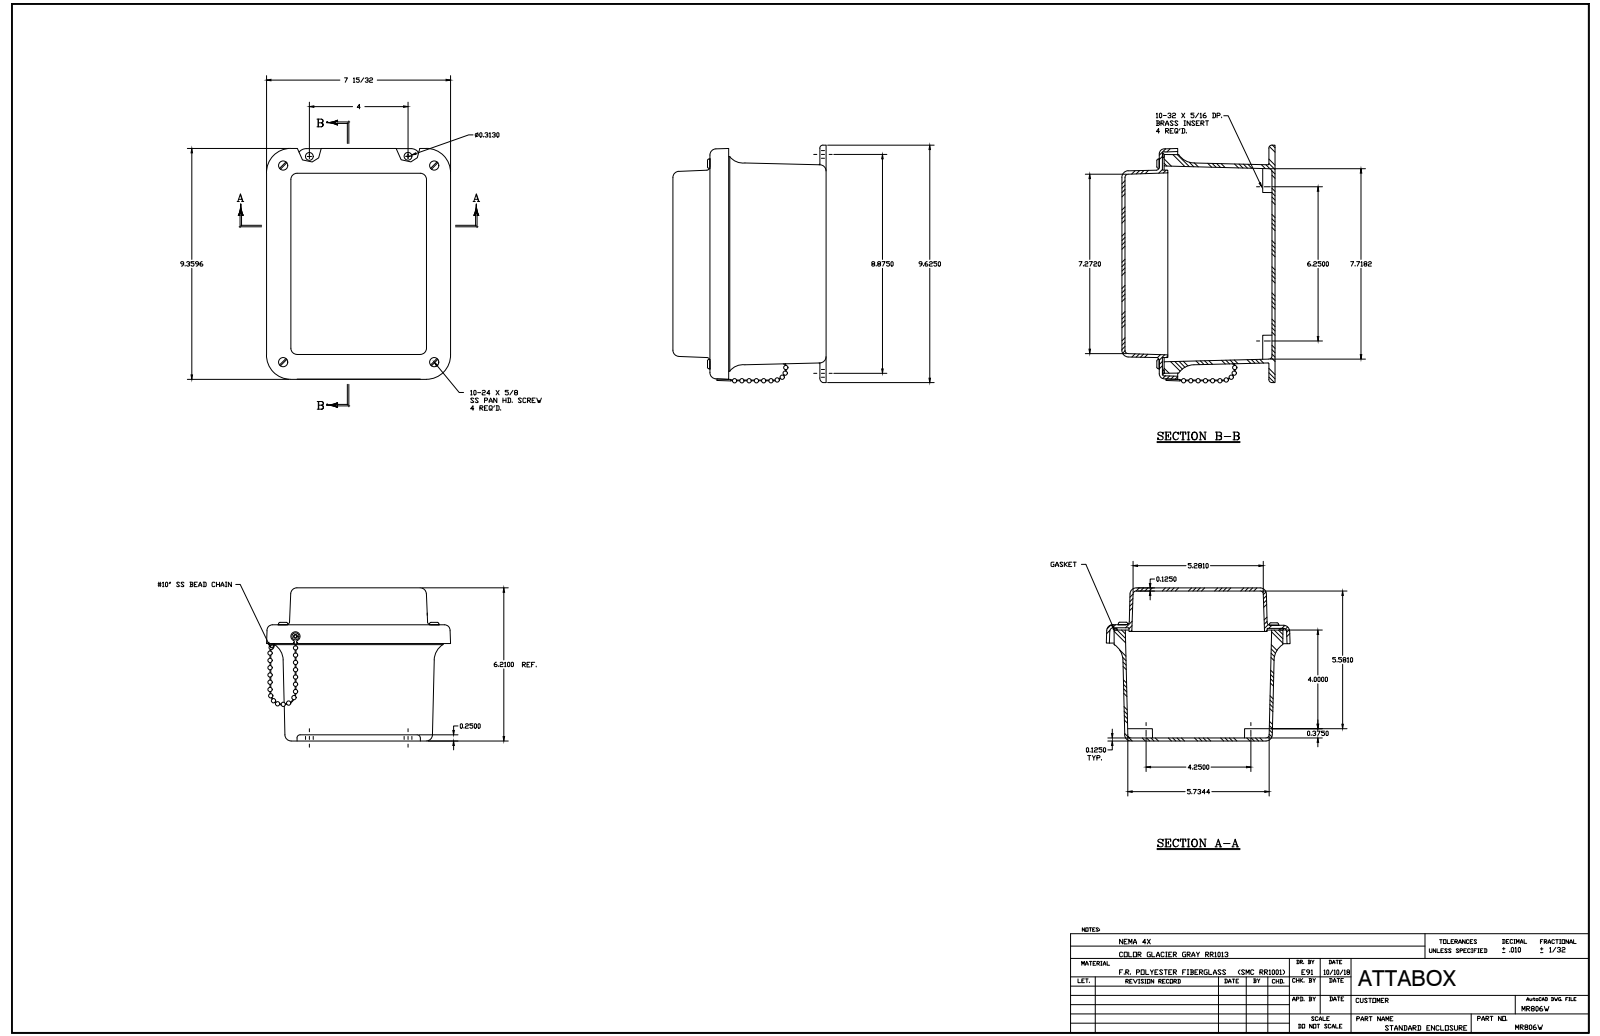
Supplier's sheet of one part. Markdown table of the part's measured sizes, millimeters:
| quantity | value |
| --- | --- |
| part name | MR806W |
| STEP written by | SolidWorks 2018 (AUTOMOTIVE_DESIGN) |
| units | millimeters |
| bodies | 45 solids, 944 faces (213 planar, 298 cylindrical, 433 other) |
| overall size | 255.3 × 195.1 × 157.5 |
| volume | 787 900 mm³ |
| surface area | 423 500 mm² |
| round holes (diameter × count) | 3.9 × 5, 3.6 × 4, 3.7 × 4, 4 × 4, 5.5 × 4, 4.7 × 2, 3.2 × 1 |
| round bosses / shafts (diameter × count) | 6.9 × 8, 4.8 × 4, 4 × 4, 9.5 × 2, 6.4 × 2, 7.2 × 1, 3.2 × 1, 3.2 × 1 |
| partial cylindrical surfaces (radius × count) | 0.8 × 20, 3.2 × 20, 6.4 × 12, 5.1 × 4, 7.9 × 4, 8 × 4, 9.5 × 4, 19.5 × 4 |
| main face-to-face distances | 3.2, 3.2, 38.5, 151.1, 112.6, 154.3, 157.5, 154.3, 115.8, 41.7 |
| hole center spacings | 33.7, 133.9, 184.1, 225.1, 108, 155.6, 158.8, 192 |
